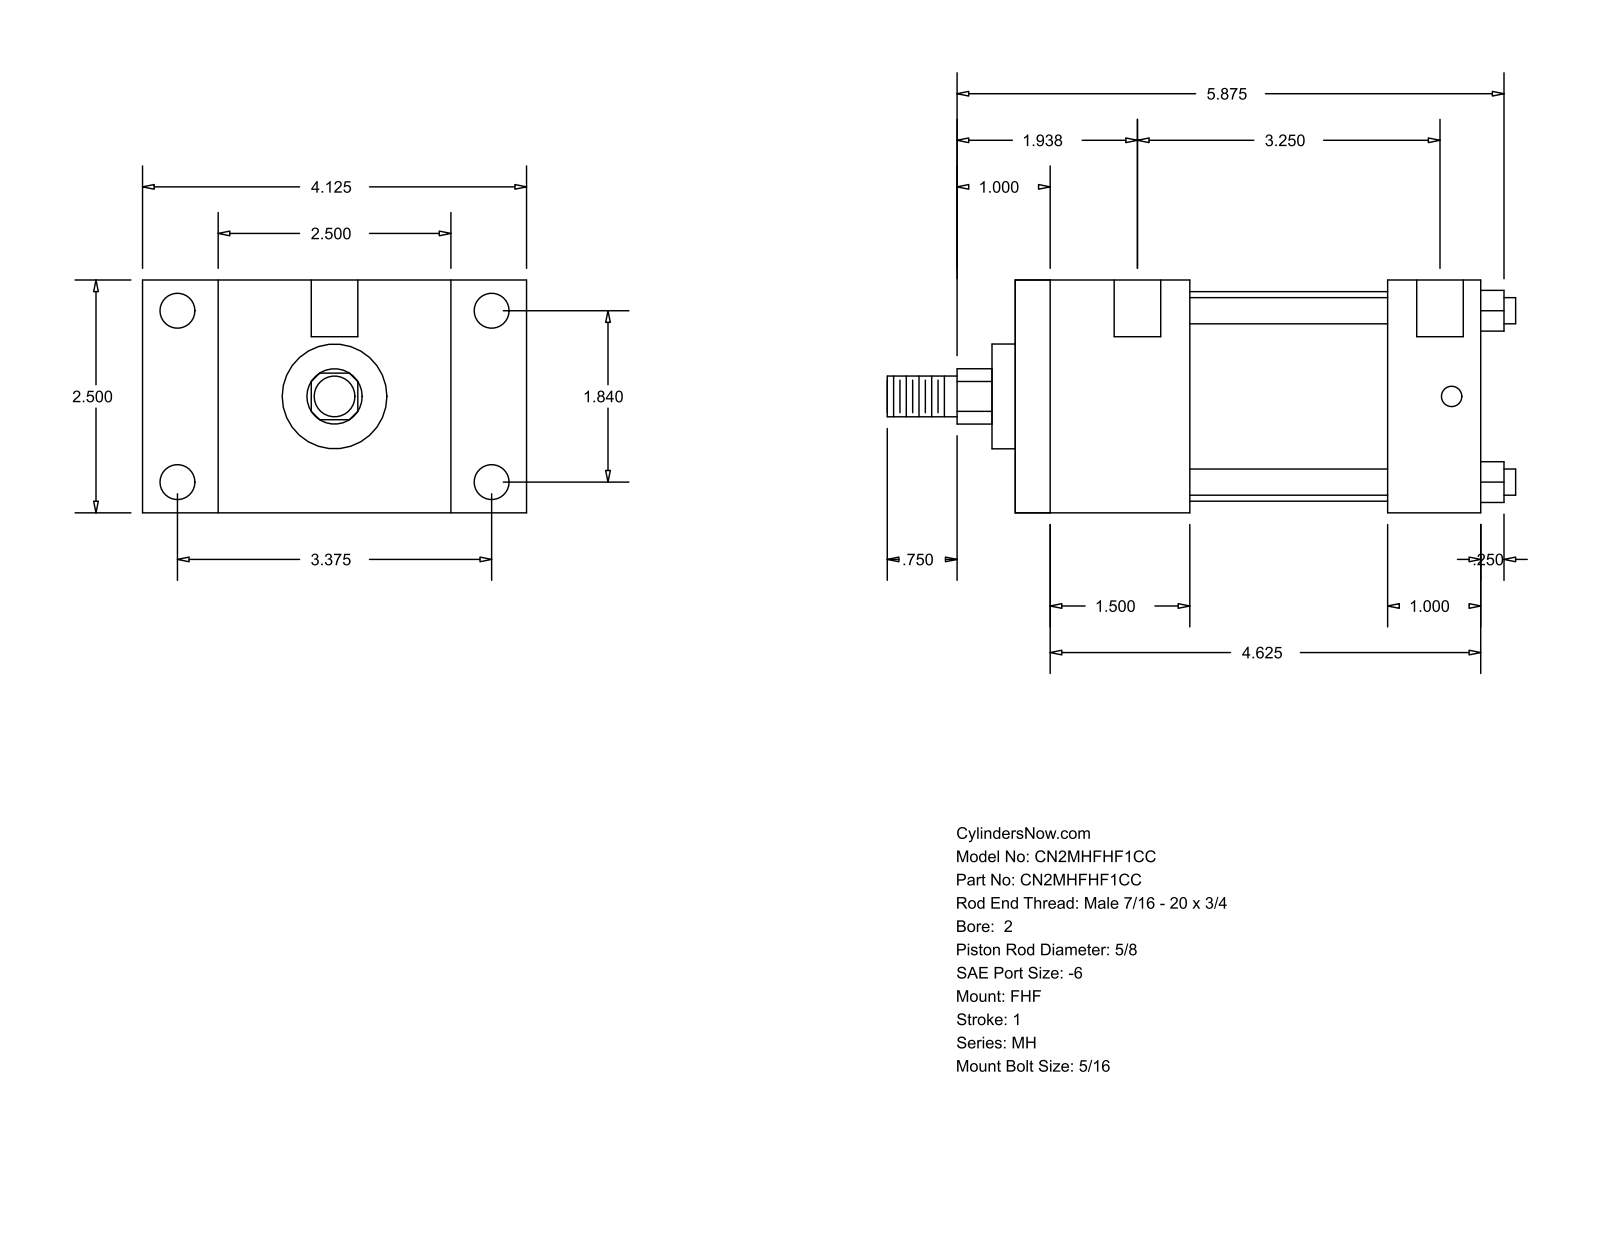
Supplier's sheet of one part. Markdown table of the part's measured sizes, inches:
| quantity | value |
| --- | --- |
| part name | MH_FHF__0200_0.625 |
| STEP written by | GSSL Pune (CONFIG_CONTROL_DESIGN) |
| units | inches |
| bodies | 0 solids, 88 faces (60 planar, 28 cylindrical, 0 other) |
| overall size | 6.75 × 4.125 × 2.5 |
| round holes (diameter × count) | 0.219 × 4, 0.375 × 4, 0.5 × 2 |
| round bosses / shafts (diameter × count) | 0.281 × 4, 2.25 × 1, 1.125 × 1, 0.625 × 1, 0.437 × 1 |
| partial cylindrical surfaces (radius × count) | 0.297 × 1 |
| main face-to-face distances | 2.5, 1.875, 5, 3.125, 0.813, 3.313, 4.125, 2.125, 4, 1 |
| hole center spacings | 1.84, 3.375, 3.563, 3.844, 0.125, 0.187, 3.25, 3.375 |
